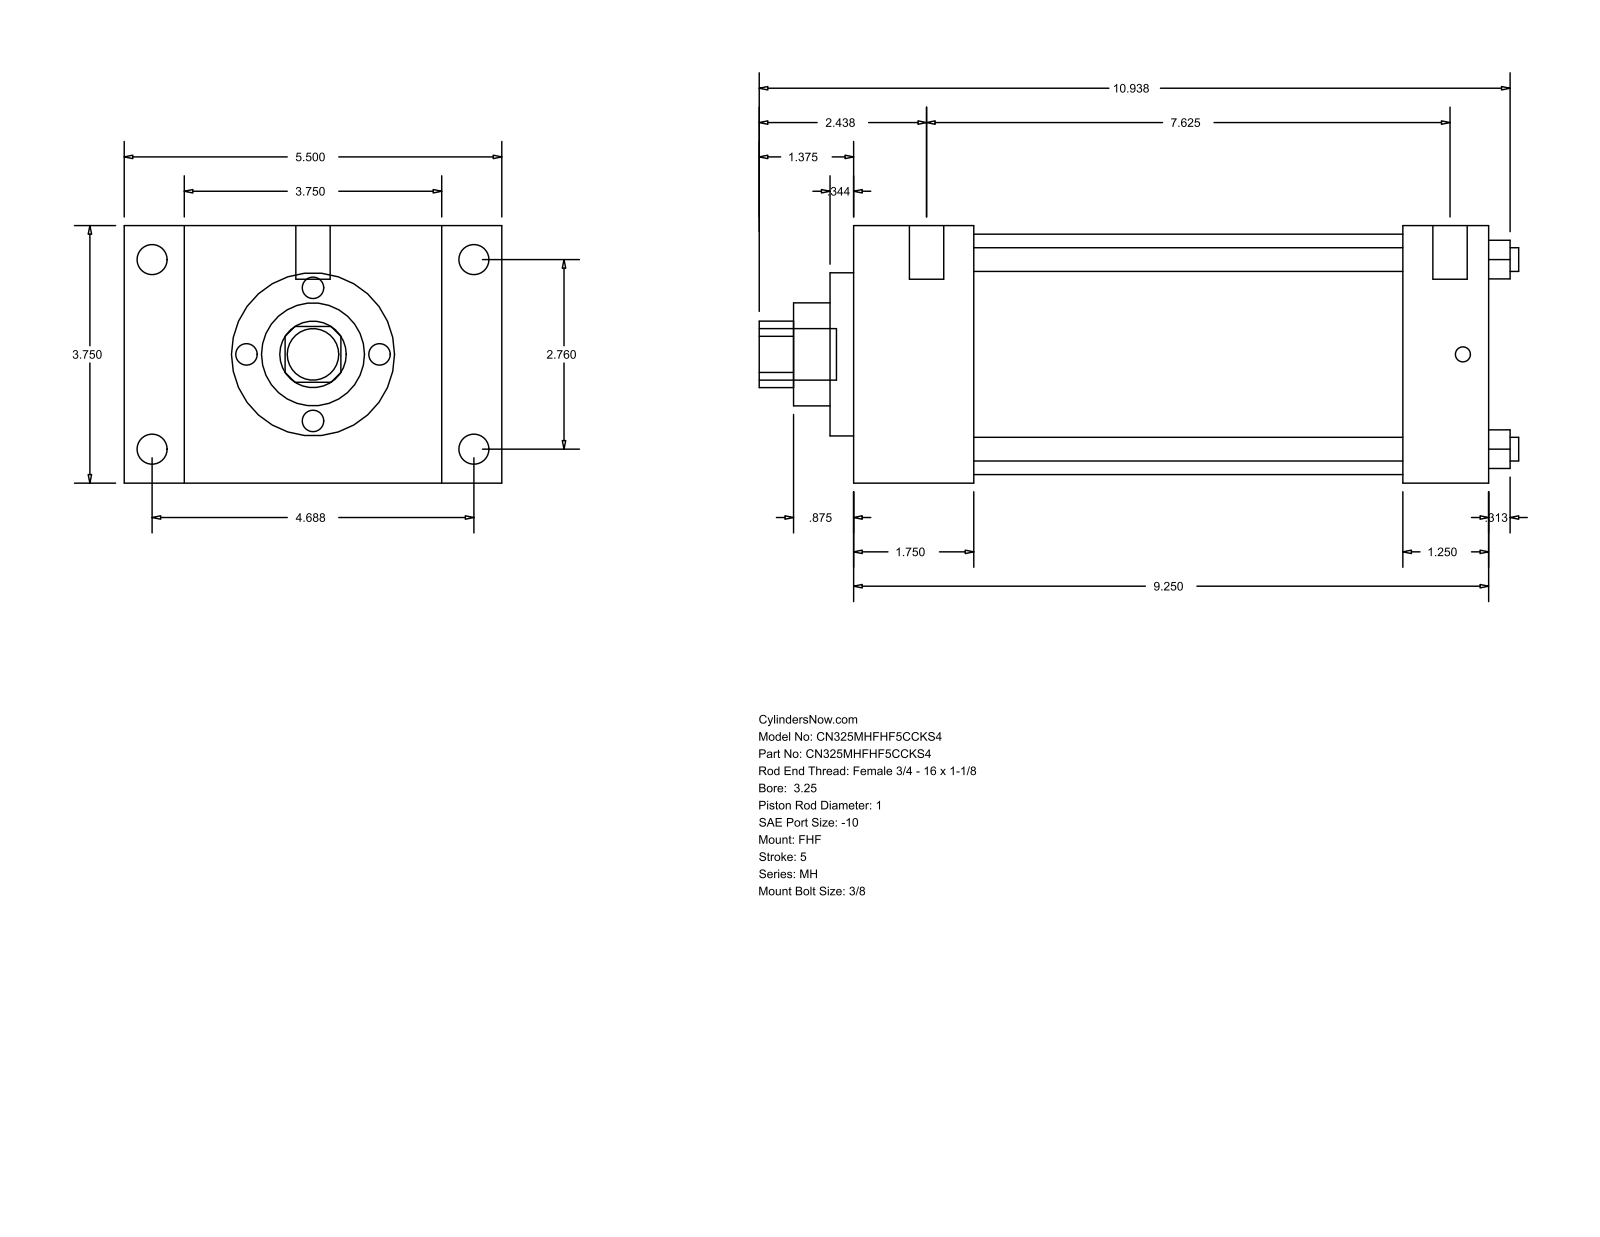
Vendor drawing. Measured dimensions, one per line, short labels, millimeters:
name: MH_FHF__0325_1
written by: GSSL Pune (CONFIG_CONTROL_DESIGN)
unit: mm
bodies: 0 solids, 90 faces (61 planar, 29 cylindrical, 0 other)
size: 280.99 × 139.7 × 95.25
holes: 4× ⌀8.76, 1× ⌀25.4, 1× ⌀38.1, 1× ⌀60.33, 1× ⌀88.9
bosses: 4× ⌀11.13, 4× ⌀5.56, 2× ⌀12.7, 1× ⌀19.05
rounds: 1× R12.29
face distances: 95.24, 234.96, 44.46, 190.5, 22.23, 117.47, 139.7, 203.2, 158.74, 31.76
hole spacings: 49.57, 70.1, 99.14
